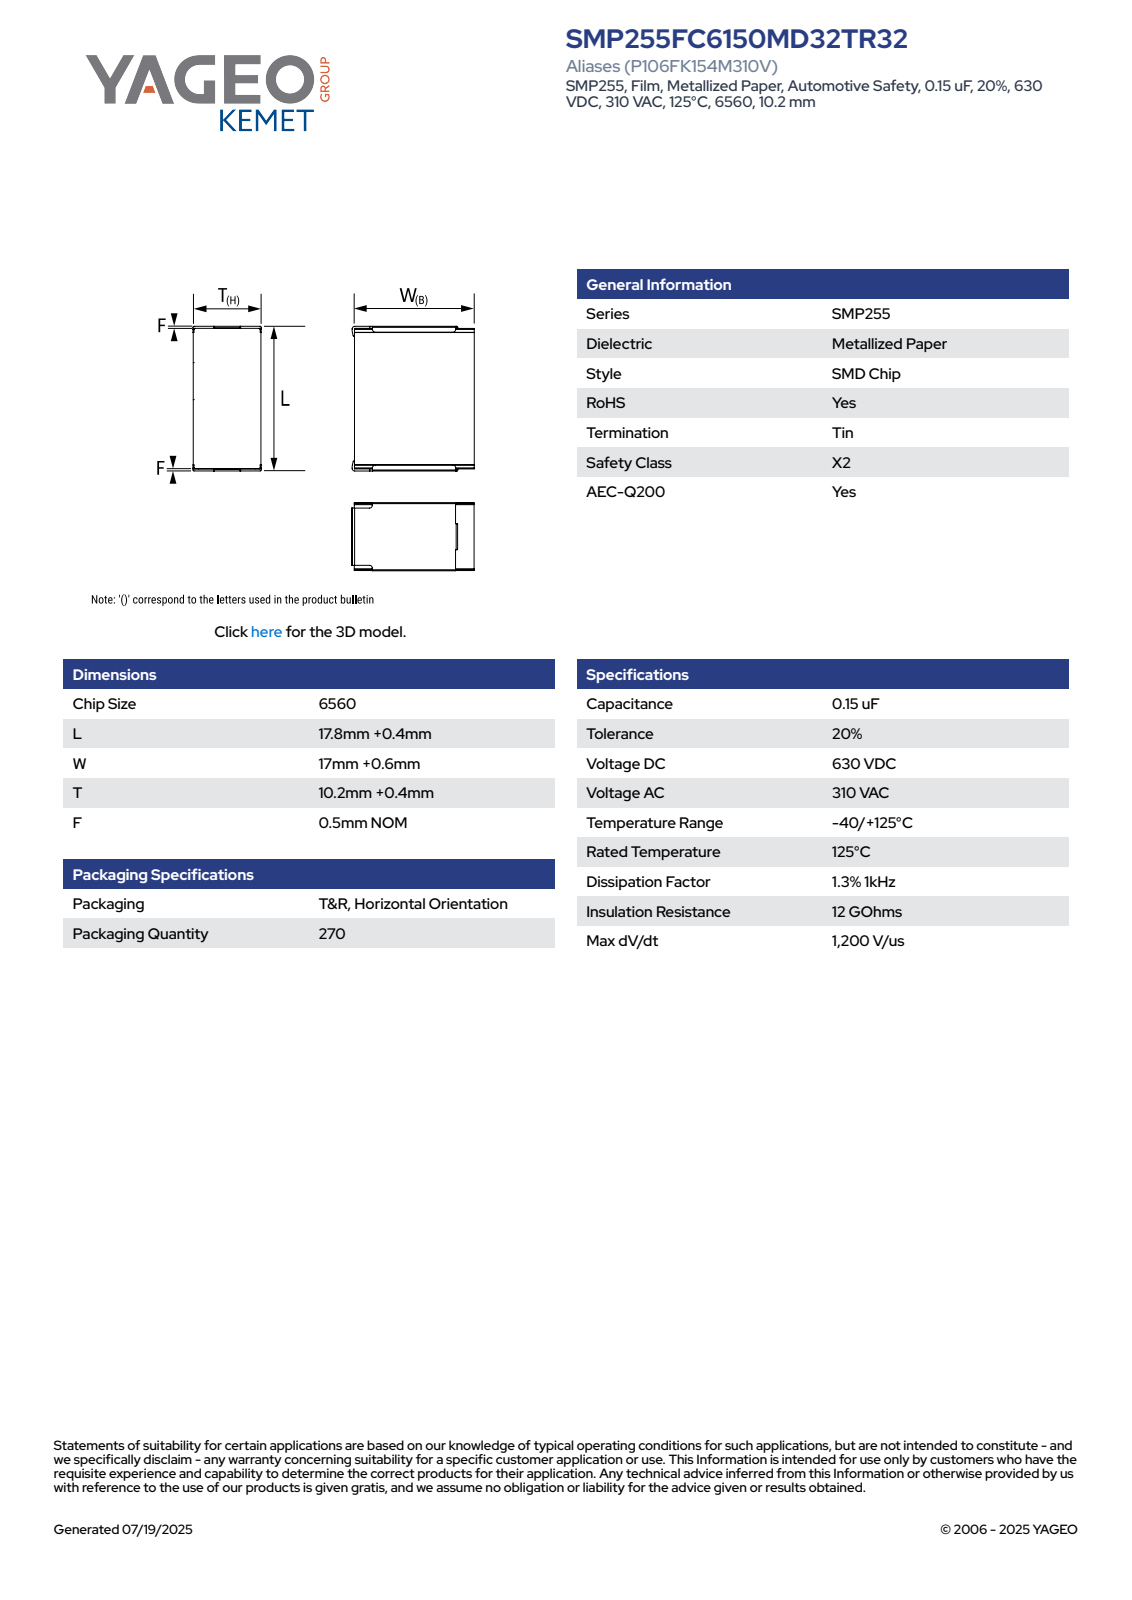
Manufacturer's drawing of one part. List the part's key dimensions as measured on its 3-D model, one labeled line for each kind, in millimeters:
Part name (STEP PRODUCT): CFS_KSTD_6560_L18.2W17.6T10.6F0.5
STEP written by: SolidWorks 2021 (AUTOMOTIVE_DESIGN)
Units: millimetres
Bodies: 4 solids, 115 faces (101 planar, 14 cylindrical, 0 other)
Overall size (bounding box): 18.2 × 18.19 × 11.14
Volume: 3 304 mm³ · Surface area: 1 485 mm²
Partial cylindrical surfaces — rounded edges, fillets, slot ends (radius × count): R0.64 ×10, R0.64 ×4
Main face-to-face distances: 10.6, 18.2, 16.9, 0.5, 17.7, 10.87, 17.2, 0.7, 11.14, 0.59
